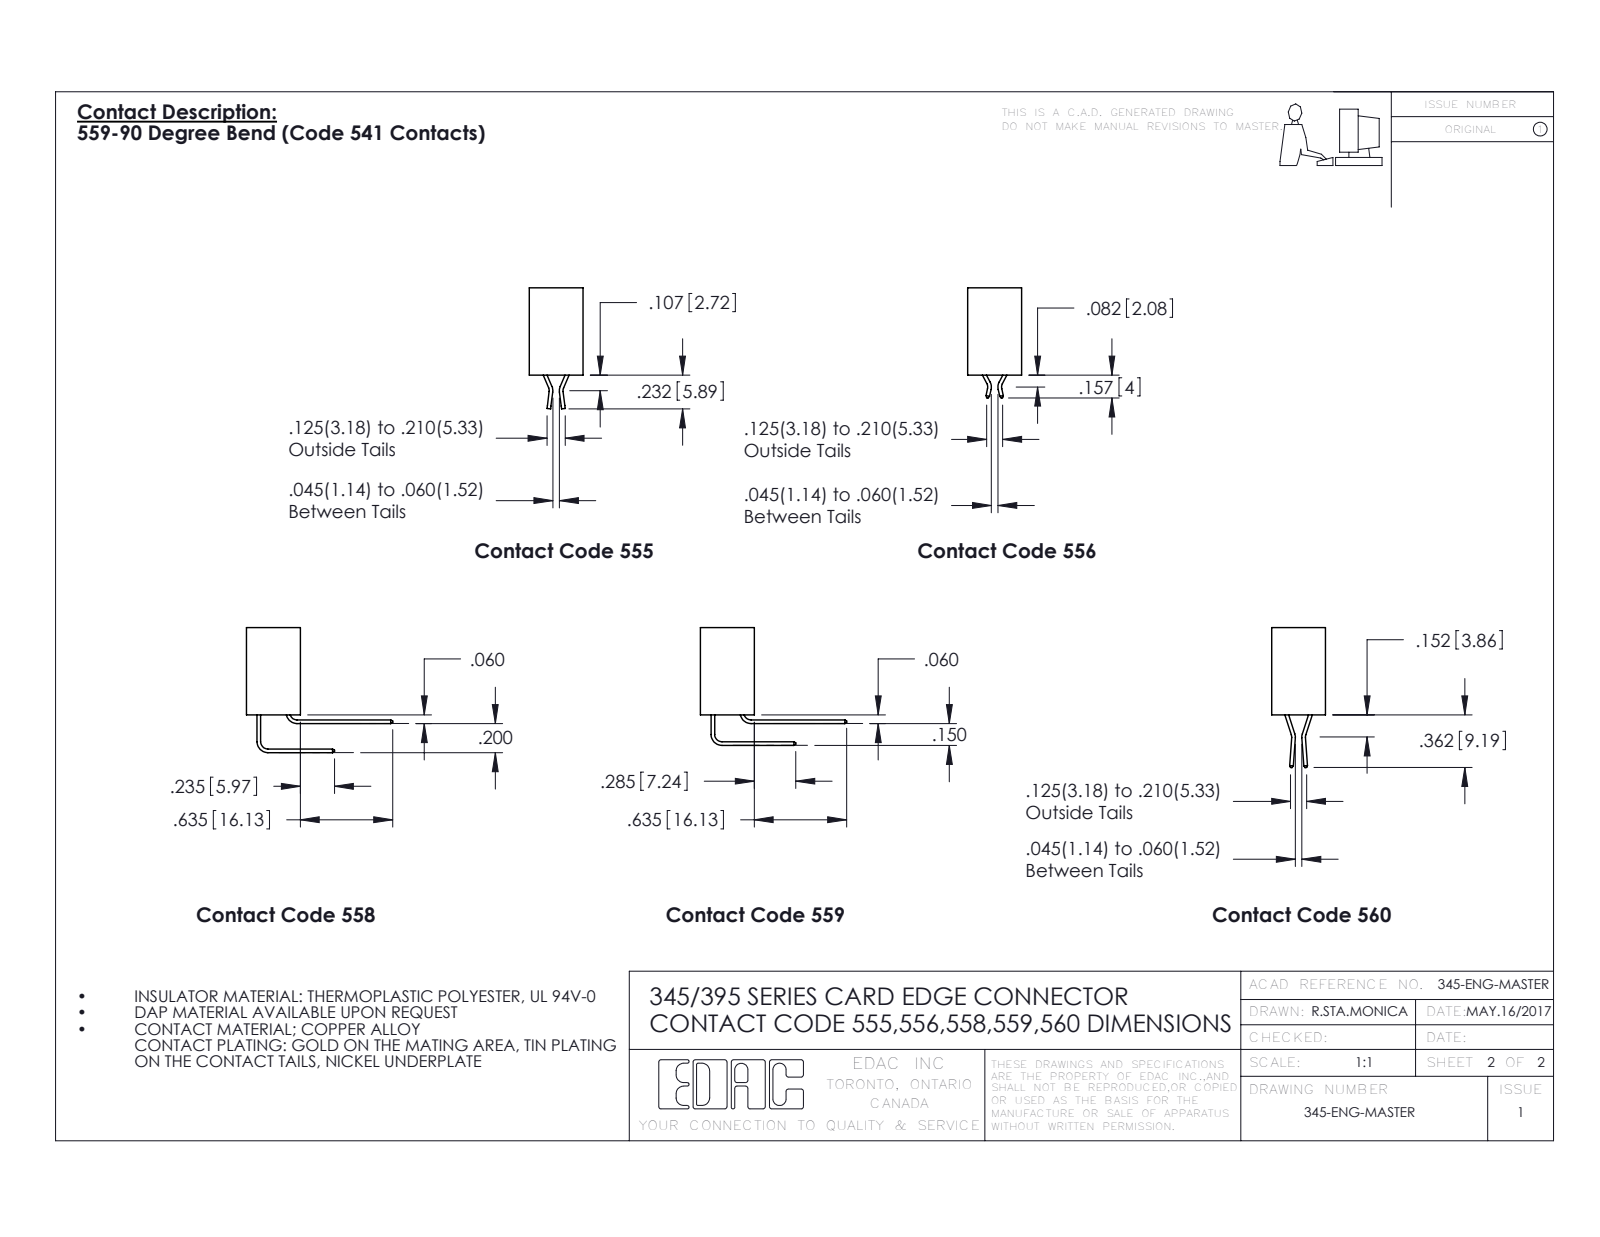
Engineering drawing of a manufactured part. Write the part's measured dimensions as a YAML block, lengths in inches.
part_name: "395-017-559-412; 345 Part_0.110 Offset - Side Mount; 345-292-001_558 559 Tail - 1"
step_written_by: "SolidWorks 2016 (CONFIG_CONTROL_DESIGN)"
units: inches
bodies: {solids: 18, faces: 1150, planar: 798, cylindrical: 352, other: 0}
overall_size: [2.535, 1.005, 0.659]
volume: 0.354
surface_area: 11.86
round_holes:
  - {diameter: 0.128, count: 2}
  - {diameter: 0.064, count: 1}
partial_cylinders:
  - {radius: 0.006, count: 34}
  - {radius: 0.01, count: 22}
  - {radius: 0.007, count: 6}
  - {radius: 0.031, count: 6}
  - {radius: 0.026, count: 3}
  - {radius: 0.031, count: 2}
  - {radius: 0.04, count: 2}
  - {radius: 0.014, count: 1}
face_to_face_distances: [0.072, 0.298, 0.37, 0.2, 0.098, 0.272, 0.025, 0.225, 0.1, 0.149]
hole_center_spacings: [2.275]
